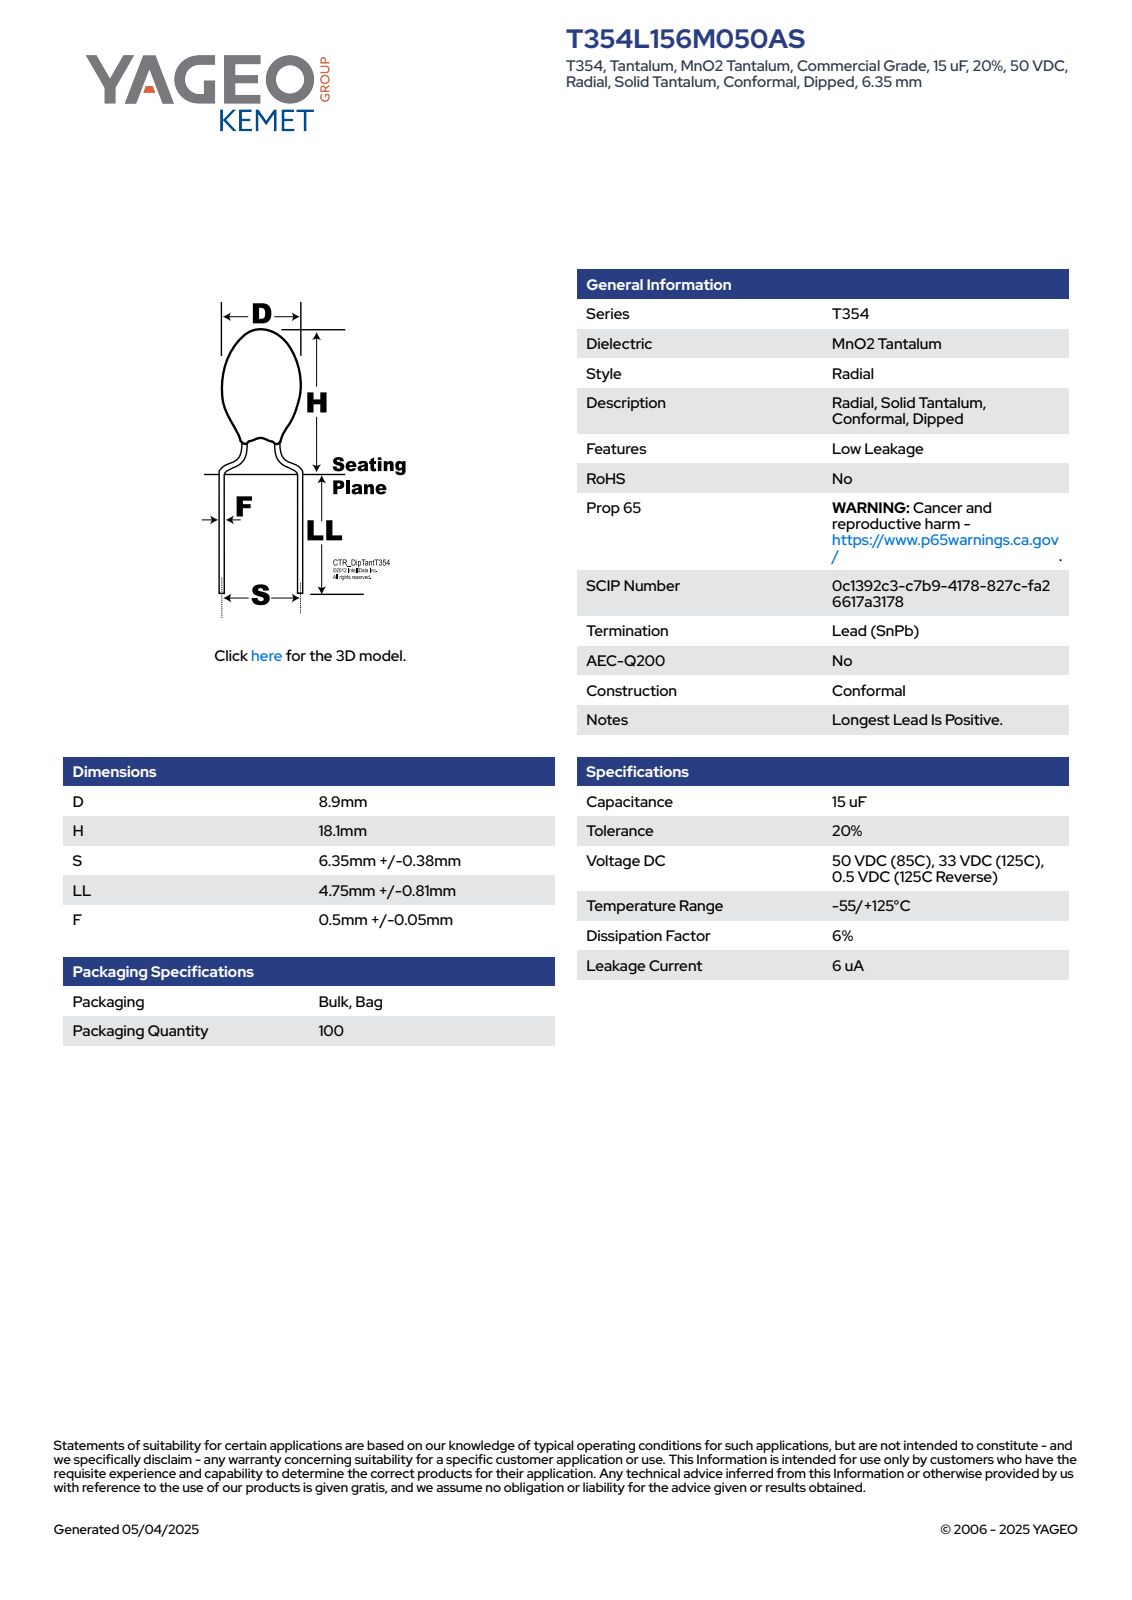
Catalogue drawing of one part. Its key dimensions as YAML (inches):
part_name: "CTR_T354_D8.9H18.1S6.35LL5.56F0.55"
step_written_by: "SolidWorks 2014 (AUTOMOTIVE_DESIGN)"
units: inches
bodies: {solids: 1, faces: 83, planar: 28, cylindrical: 10, other: 45}
overall_size: [0.931, 0.35, 0.35]
volume: 0.04
surface_area: 0.651
round_bosses_or_shafts:
  - {diameter: 0.022, count: 2}
  - {diameter: 0.35, count: 1}
partial_cylinders:
  - {radius: 0.175, count: 1}
face_to_face_distances: [0.497, 0.434, 0.931, 0.754, 0.319, 0.178, 0.706, 0.272, 0.048, 0.226]
